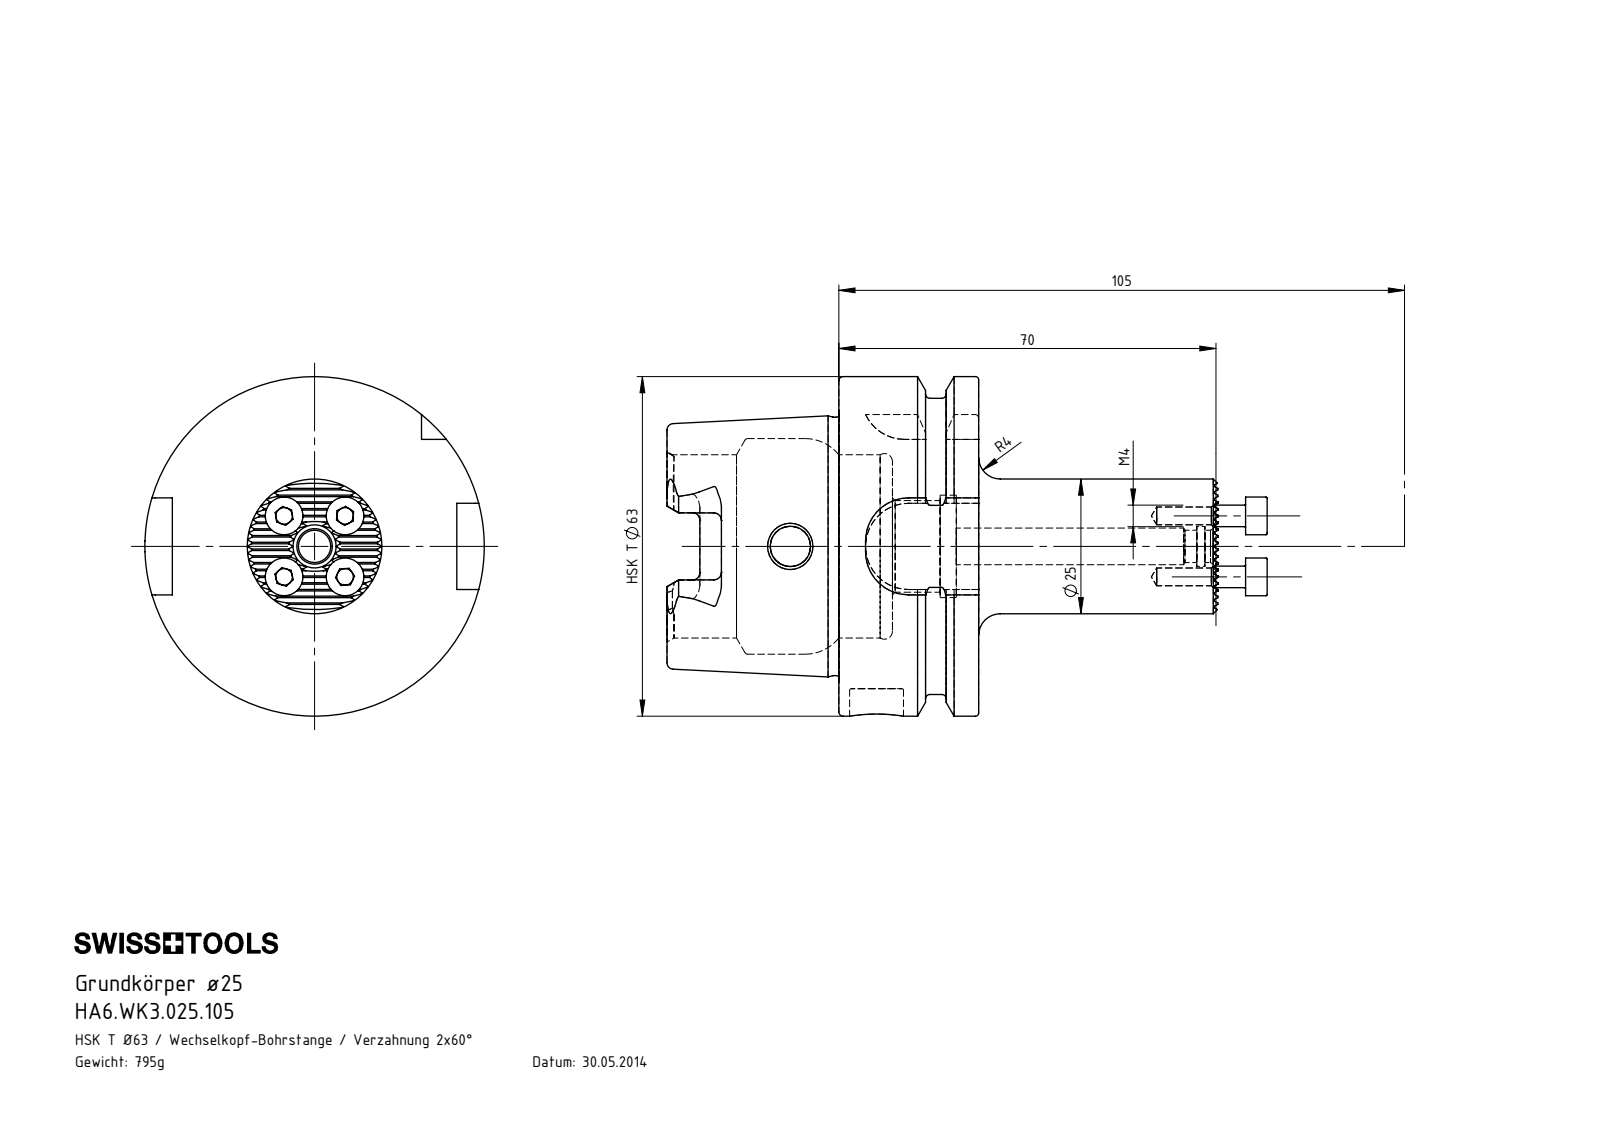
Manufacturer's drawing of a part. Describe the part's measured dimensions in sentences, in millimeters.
The part is named "DIN 3771 - 6x1; ISO 4762 - M4 x 12; HA6.WK3.025.105; HA6-WK3.025.105_A". Its 3-D file was written by "SolidWorks 2017 (AUTOMOTIVE_DESIGN)". It is 6 solids with 486 faces: 238 planar, 117 cylindrical and 131 other. Overall it measures 111.4 by 63 by 63 millimeters. Its volume is 102 328 cubic millimeters and its surface area 28 499 square millimeters. Round holes: 4 of diameter 3.3, 1 of diameter 6, 1 of diameter 6.8, 1 of diameter 7.4, 1 of diameter 7.5, 1 of diameter 10, 1 of diameter 17, 1 of diameter 19, 1 of diameter 34, 1 of diameter 40. Round bosses or shafts: 4 of diameter 7, 4 of diameter 4, 1 of diameter 63, 1 of diameter 54.95, 1 of diameter 47.94, 1 of diameter 25. Partial cylindrical surfaces (rounded edges, fillets, slot ends): 19 of radius 0.12, 6 of radius 1.4, 4 of radius 2.88, 4 of radius 8. The main face-to-face distances are 25.95, 16, 9.95, 31.9, 41.85, 57.85, 53.7, 21.8, 52.8, 11.85. The hole center spacings are 8, 11.32, 16.01.
